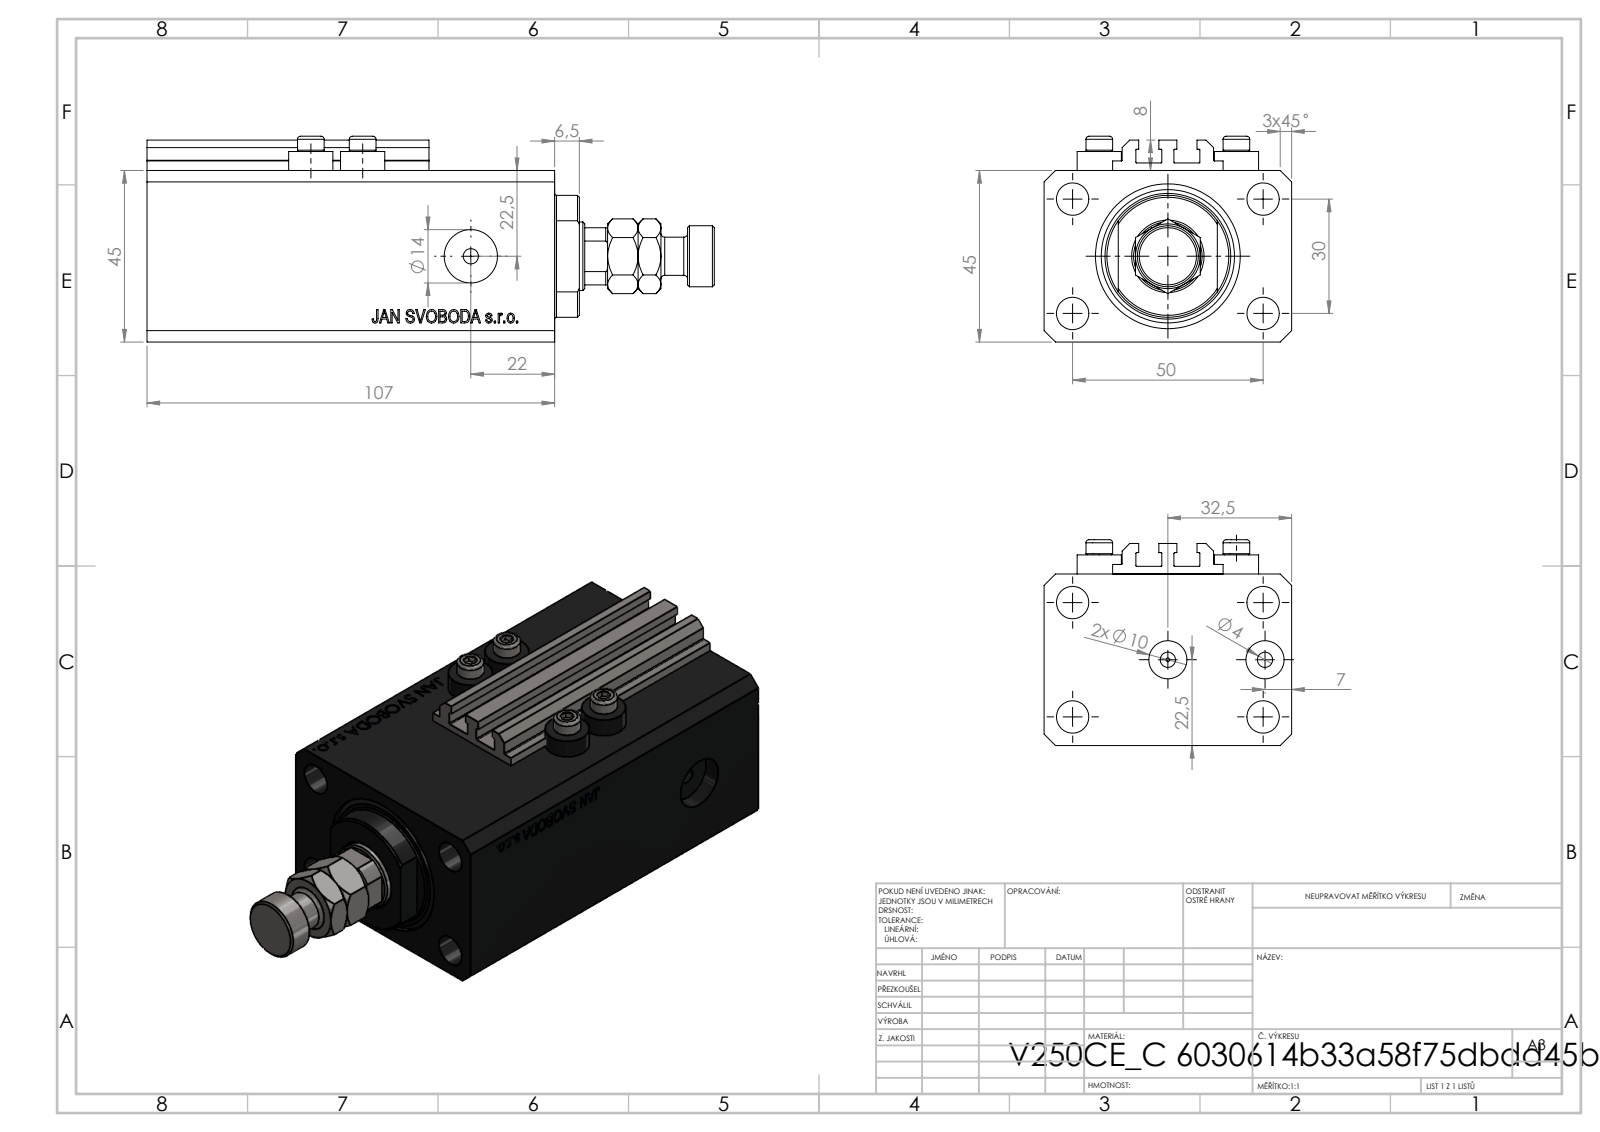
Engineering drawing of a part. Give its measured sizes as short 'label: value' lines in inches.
name: MFA; V250CE_C_Body; V250CE_C_VCP; ALLEN BOLT V250CE (+2 more)
written by: SolidWorks 2019 (CONFIG_CONTROL_DESIGN)
unit: in
bodies: 11 solids, 1142 faces (552 planar, 104 cylindrical, 486 other)
size: 7.283 × 2.559 × 2.126
volume: 18.16 in³; area: 122.8 in²
holes: 8× ⌀0.157, 5× ⌀0.335, 2× ⌀0.394, 2× ⌀0.551, 1× ⌀0.049, 1× ⌀0.709, 1× ⌀0.984, 1× ⌀1.496
bosses: 4× ⌀0.457, 4× ⌀0.276, 2× ⌀0.268, 2× ⌀0.256, 2× ⌀0.157, 1× ⌀0.63
rounds: 10× R0.008, 1× R0.335, 1× R0.63
face distances: 1.772, 2.559, 0.551, 1.85, 4.213, 3.661, 0.118, 0.079, 0.272, 0.807
hole spacings: 1.148, 0.535, 0.591, 1.181, 1.417, 1.515, 1.969, 2.074
